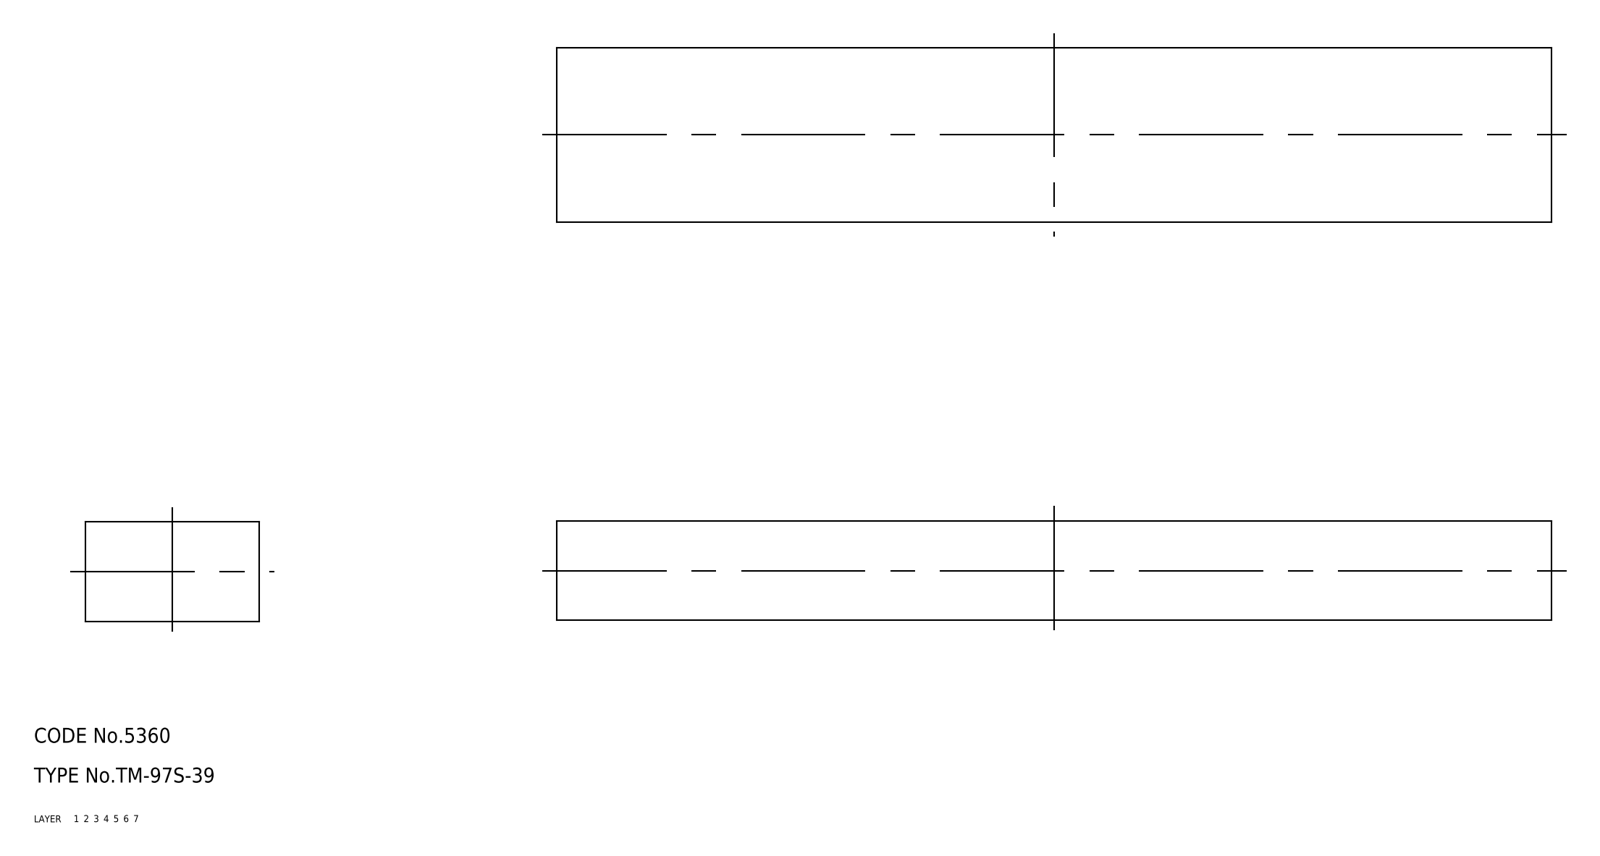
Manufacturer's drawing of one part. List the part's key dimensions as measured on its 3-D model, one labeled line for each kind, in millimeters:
Part name (STEP PRODUCT): rubber foam
STEP written by: CADfix (AUTOMOTIVE_DESIGN)
Units: millimetres
Bodies: 1 solid, 6 faces (0 planar, 0 cylindrical, 6 other)
Overall size (bounding box): 200 × 35 × 20
Volume: 140 000 mm³ · Surface area: 23 400 mm²
